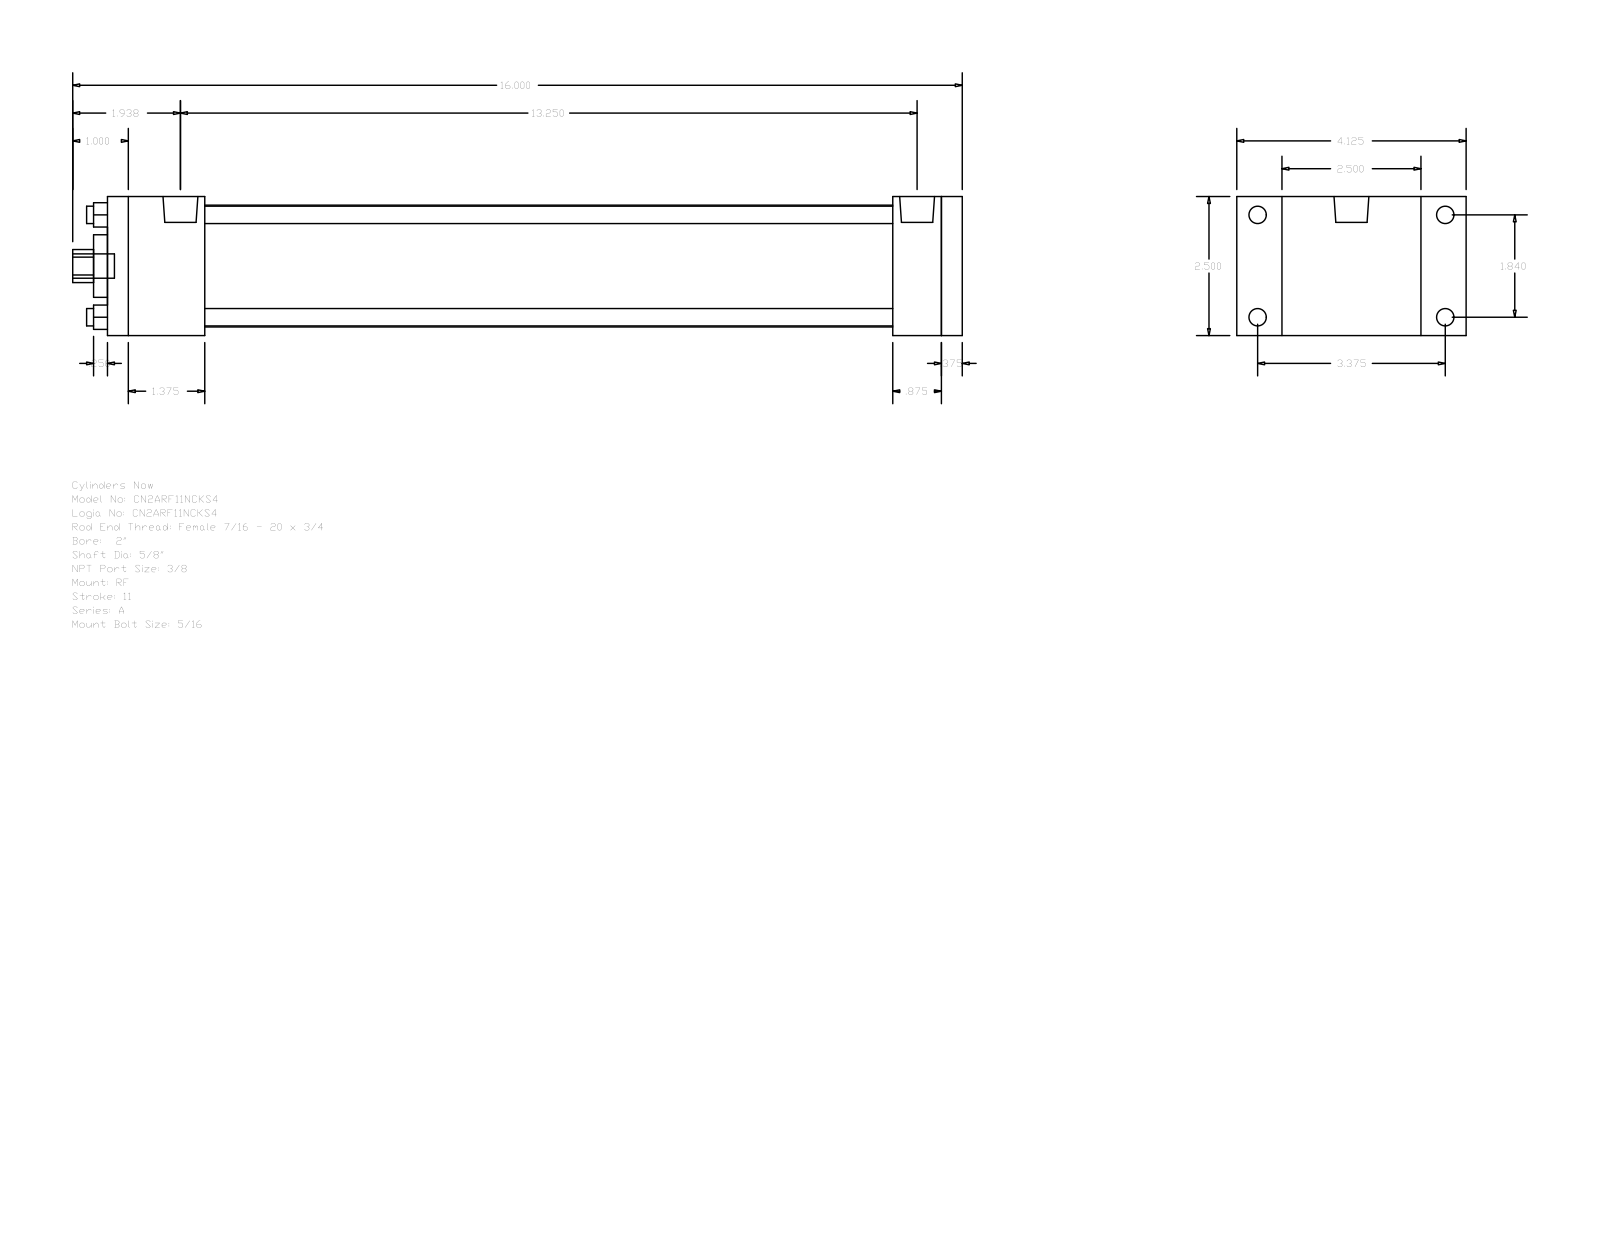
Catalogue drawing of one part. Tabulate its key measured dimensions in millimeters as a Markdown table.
| quantity | value |
| --- | --- |
| part name | A_RF__0200_0.625 |
| STEP written by | GSSL Pune (CONFIG_CONTROL_DESIGN) |
| units | millimeters |
| bodies | 0 solids, 92 faces (64 planar, 28 cylindrical, 0 other) |
| overall size | 406.4 × 104.78 × 63.5 |
| round holes (diameter × count) | 7.94 × 4, 15.88 × 1, 28.57 × 1, 55.63 × 1 |
| round bosses / shafts (diameter × count) | 7.94 × 4, 5.56 × 4, 15.93 × 2, 11.11 × 1 |
| partial cylindrical surfaces (radius × count) | 7.54 × 1 |
| main face-to-face distances | 63.5, 390.52, 9.52, 381, 44.45, 336.55, 346.07, 358.77, 314.32, 22.23 |
| hole center spacings | 33.05, 46.74, 66.1 |
